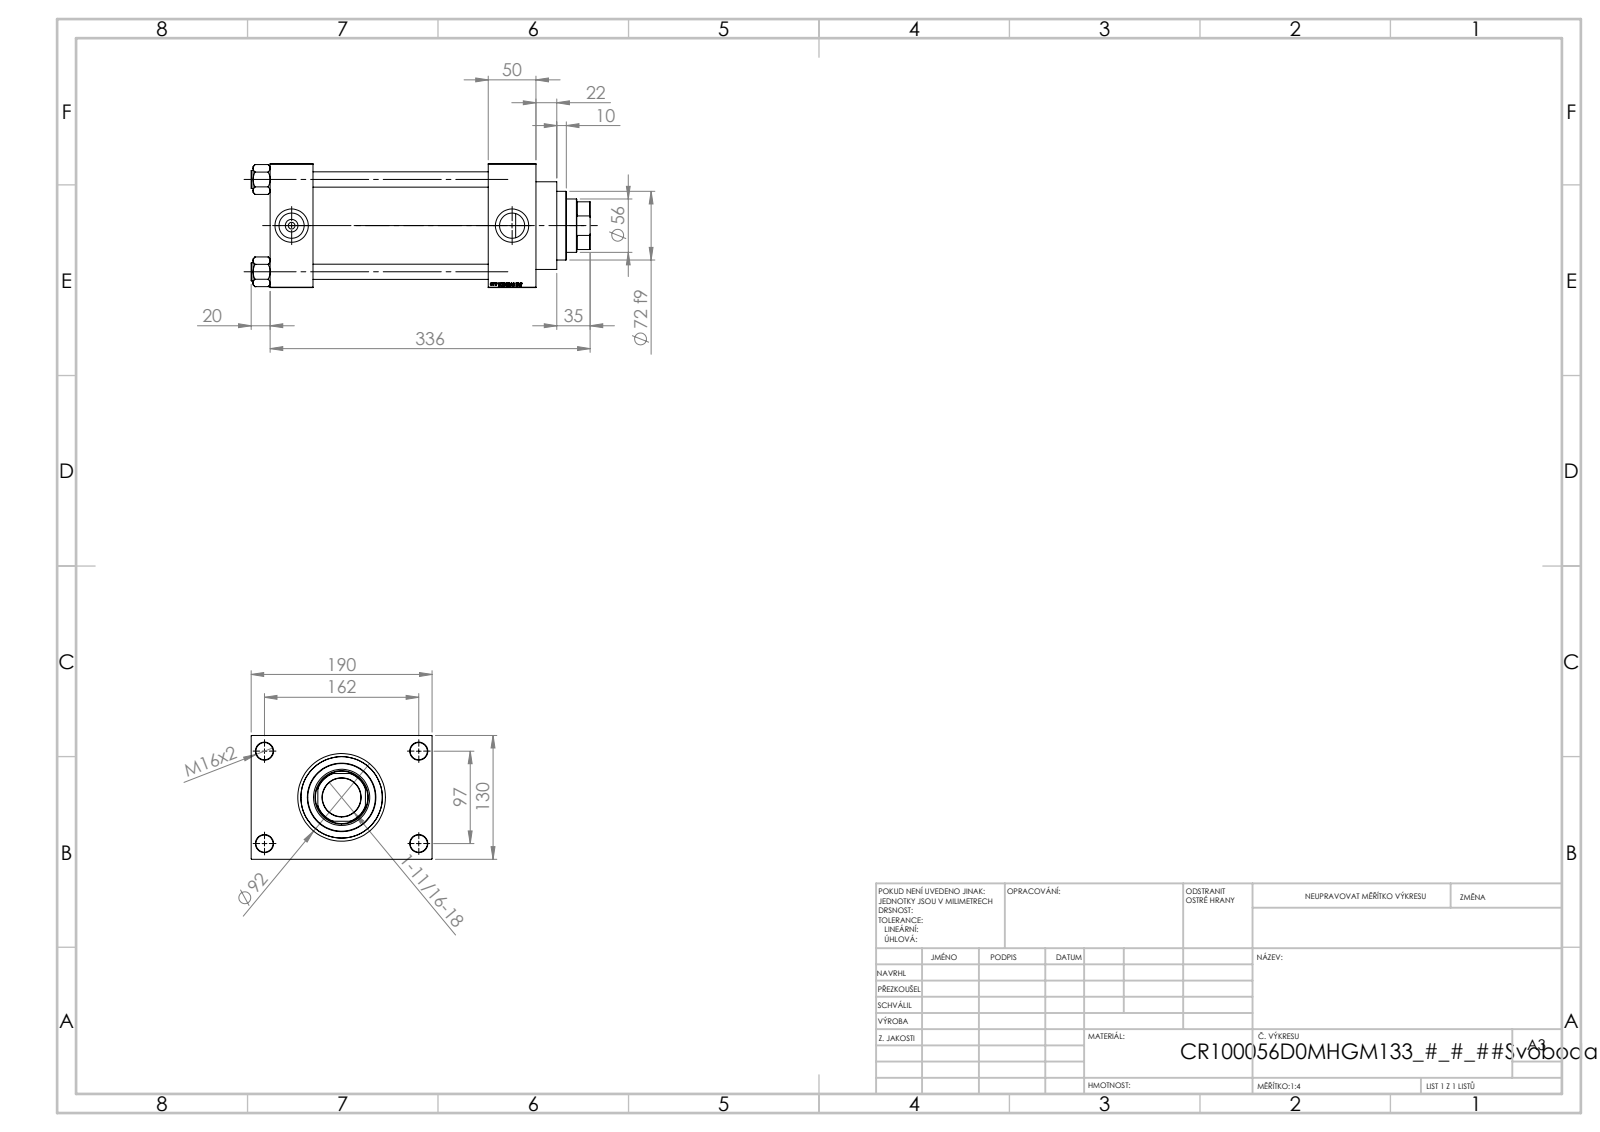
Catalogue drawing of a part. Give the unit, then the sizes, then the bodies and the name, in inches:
Units: inches
Overall size (bounding box): 14.016 × 7.48 × 5.118
Round holes (diameter × count): ⌀0.63 ×4, ⌀0.709 ×4, ⌀0.276 ×2, ⌀1.041 ×2, ⌀1.378 ×2, ⌀1.594 ×1, ⌀2.205 ×1, ⌀2.323 ×1, ⌀2.992 ×1, ⌀3.366 ×1, ⌀3.937 ×1
Round bosses / shafts (diameter × count): ⌀0.748 ×4, ⌀4.173 ×1, ⌀3.622 ×1, ⌀2.835 ×1
Partial cylindrical surfaces — rounded edges, fillets, slot ends (radius × count): R1.063 ×1
Main face-to-face distances: 5.118, 1.969, 1.772, 9.016, 7.244, 10.984, 9.213, 1.181, 6.299, 7.48
Hole centre spacings: 1.281, 2.698, 3.717, 3.815, 4.026, 5.096, 6.367, 3.819
Volume: 189.6 in³ · Surface area: 741 in²
Bodies: 11 solids, 1151 faces (545 planar, 88 cylindrical, 518 other)
Part name (STEP PRODUCT): V215CR_D_Body; V215CR_VCP_D; NUT_M5_D; V215_VC_A (+1 more)
STEP written by: SolidWorks 2019 (CONFIG_CONTROL_DESIGN)
